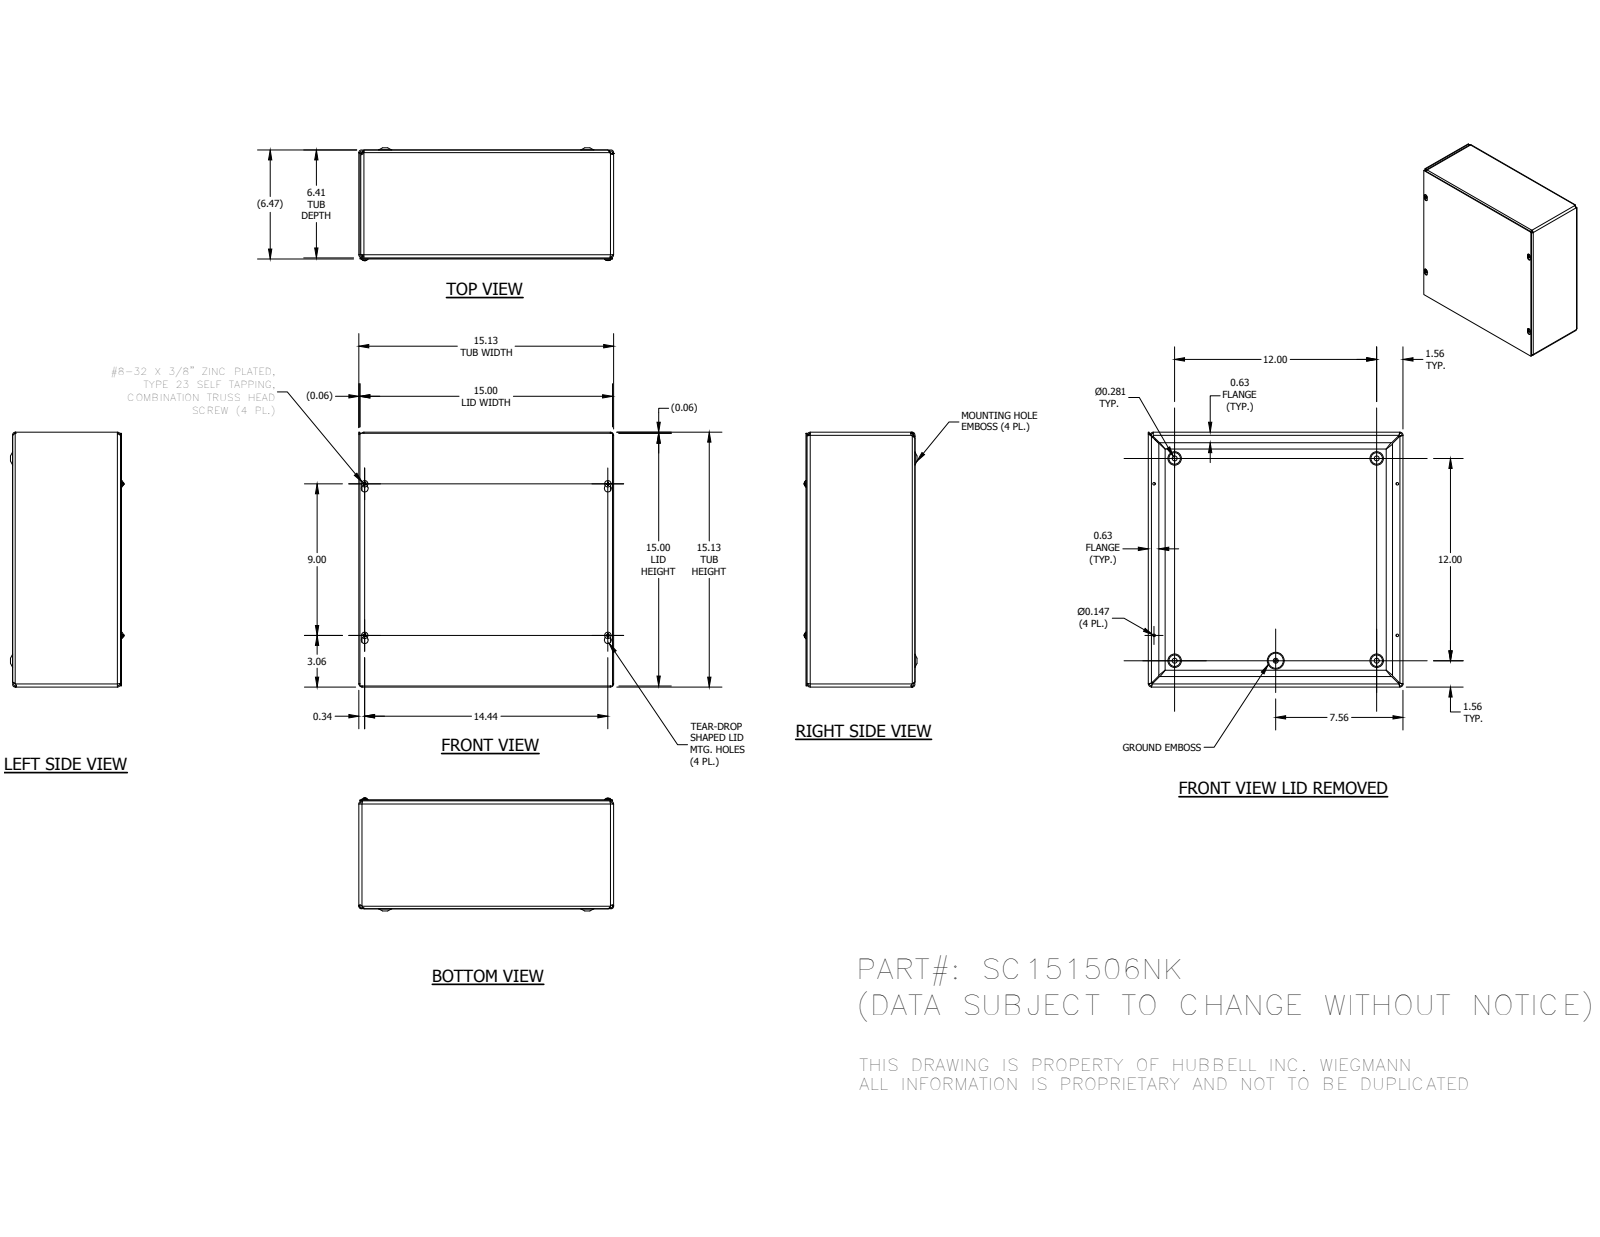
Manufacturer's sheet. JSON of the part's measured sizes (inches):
{"part_name": "SC1515BKP; SC151506NKWRA; SC1515LID; 34056 (+1 more)", "step_written_by": "Autodesk Inventor 2014 (AUTOMOTIVE_DESIGN)", "units": "inches", "bodies": {"solids": 7, "faces": 357, "planar": 132, "cylindrical": 67, "other": 158}, "overall_size": [15.125, 15.125, 6.693], "volume_in3": 56.22, "surface_area_in2": 1827, "round_holes": [[0.147, 4], [0.3, 4], [0.165, 1]], "round_bosses_or_shafts": [[0.384, 4], [0.164, 4], [0.228, 1]], "partial_cylinders_radius": [[0.125, 12], [0.187, 8], [0.055, 4], [0.062, 4], [0.094, 4], [0.117, 4], [0.124, 4], [0.156, 4]], "face_to_face_distances": [0.062, 15.063, 6.343, 6.405, 0.063, 6.406, 6.468, 15.125, 15.001, 0.124], "hole_center_spacings": [1.933, 10.57, 12, 16.881, 6, 9, 12.742, 13.303]}
